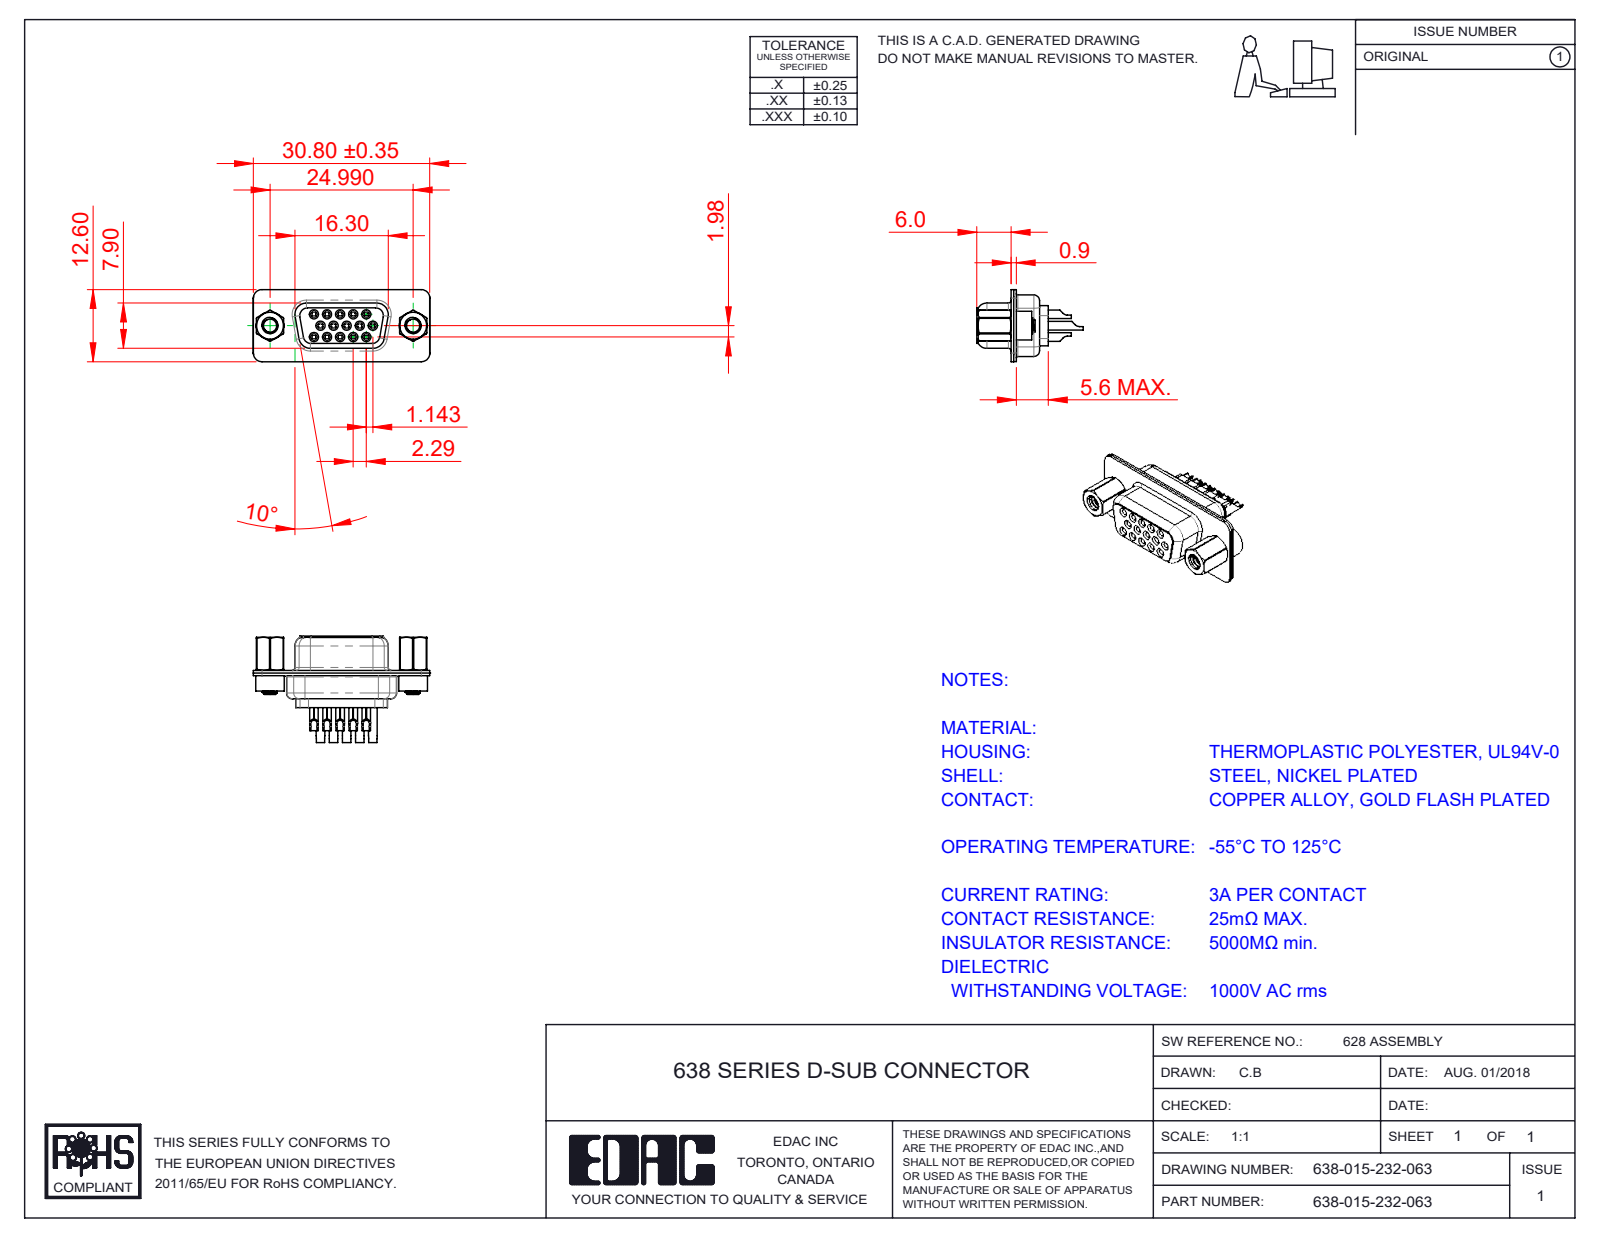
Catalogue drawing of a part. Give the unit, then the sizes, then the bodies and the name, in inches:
Units: inches
Overall size (bounding box): 1.213 × 0.732 × 0.496
Round holes (diameter × count): ⌀0.031 ×15, ⌀0.039 ×15, ⌀0.043 ×15, ⌀0.063 ×15, ⌀0.067 ×15, ⌀0.071 ×15, ⌀0.079 ×2, ⌀0.089 ×2, ⌀0.09 ×2, ⌀0.157 ×2, ⌀0.159 ×2, ⌀0.191 ×2
Round bosses / shafts (diameter × count): ⌀0.079 ×15, ⌀0.059 ×15, ⌀0.047 ×15, ⌀0.197 ×2, ⌀0.195 ×2, ⌀0.189 ×2, ⌀0.11 ×2
Partial cylindrical surfaces — rounded edges, fillets, slot ends (radius × count): R0.059 ×20, R0.079 ×12, R0.011 ×10, R0.061 ×8, R0.039 ×7, R0.053 ×5, R0.01 ×4, R0.02 ×4
Main face-to-face distances: 0.018, 0.035, 0.016, 0.056, 0.35, 0.26, 0.055, 0.09, 0.244, 0.033
Hole centre spacings: 0.156, 0.09, 0.18, 0.09, 0.238, 0.238, 0.27, 0.312
Volume: 0.111 in³ · Surface area: 9.833 in²
Bodies: 22 solids, 1740 faces (404 planar, 584 cylindrical, 752 other)
Part name (STEP PRODUCT): 638 Shell Front_15 Contacts; 638 Housing_15 Contacts; 638 Contact Row 3_32; 638-015-232-063 (+5 more)
STEP written by: SolidWorks 2020 (CONFIG_CONTROL_DESIGN)
